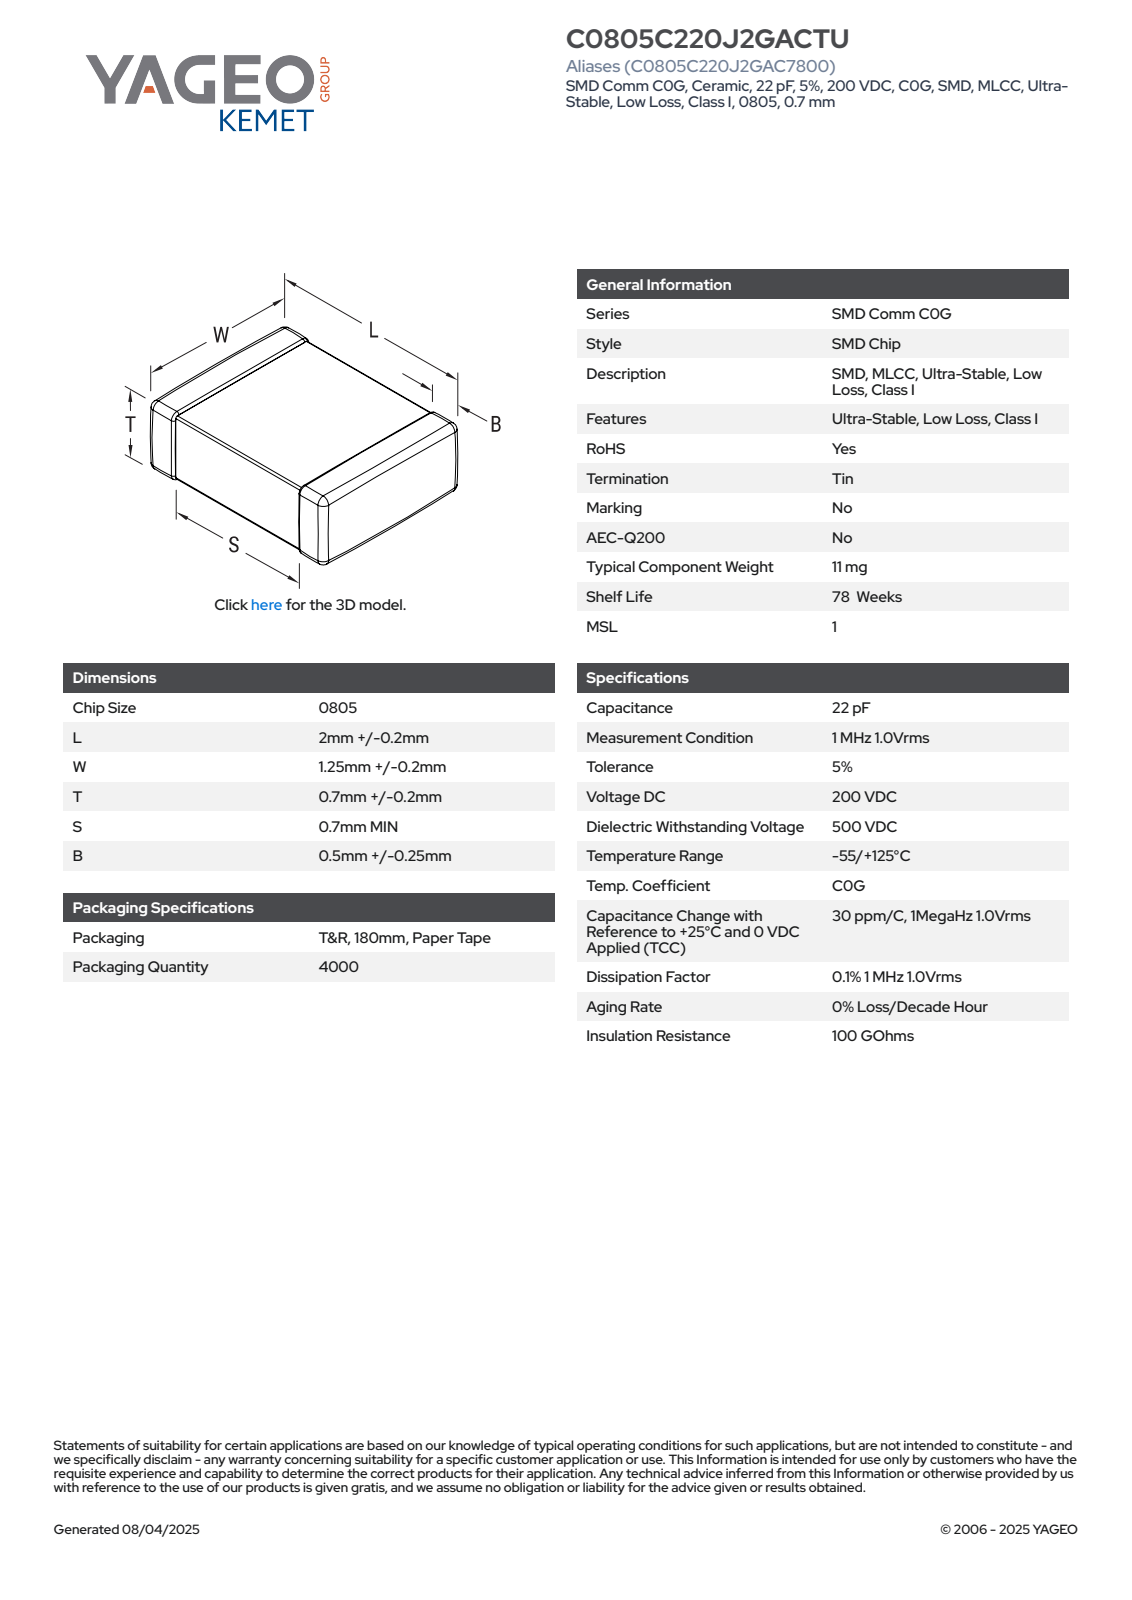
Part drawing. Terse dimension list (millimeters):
name: CCS_CCSTD_0805_L2.2W1.45T0.9B0.5
written by: SolidWorks 2014 (AUTOMOTIVE_DESIGN)
unit: mm
bodies: 4 solids, 125 faces (71 planar, 38 cylindrical, 16 other)
size: 2.2 × 1.45 × 0.9
volume: 3 mm³; area: 13 mm²
face distances: 0.87, 0.84, 1.42, 0.9, 2.2, 1.39, 1.45, 0.97, 1.23, 1.19
